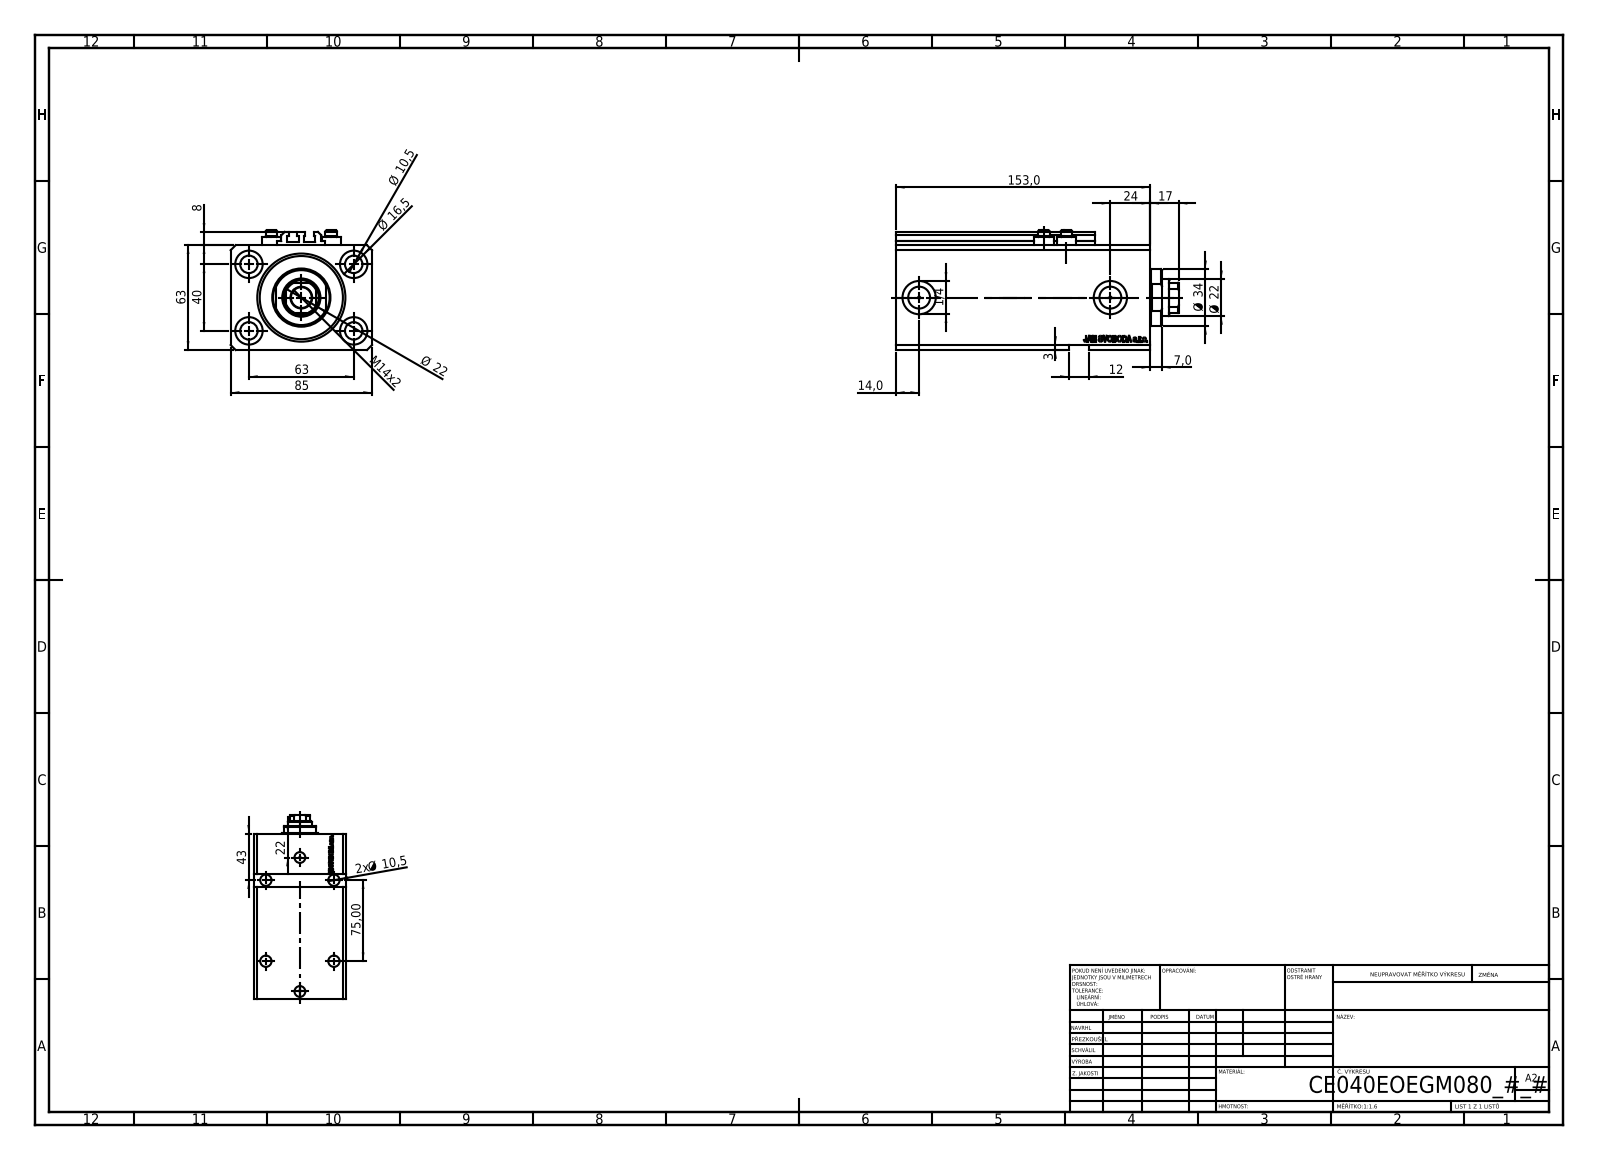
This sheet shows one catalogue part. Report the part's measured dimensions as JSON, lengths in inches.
{"part_name": "V250CE_E_Body; V250CE_C_VCP; V250CE_VC_E; ALLEN BOLT V250CE", "step_written_by": "SolidWorks 2019 (CONFIG_CONTROL_DESIGN)", "units": "inches", "bodies": {"solids": 8, "faces": 1107, "planar": 535, "cylindrical": 146, "other": 426}, "overall_size": [6.693, 3.346, 2.835], "volume_in3": 41.73, "surface_area_in2": 218.3, "round_holes": [[0.413, 8], [0.049, 4], [0.157, 4], [0.65, 4], [0.394, 2], [0.518, 2], [0.787, 2], [0.492, 1], [0.866, 1], [1.575, 1], [2.087, 1]], "round_bosses_or_shafts": [[0.457, 4], [0.276, 4], [1.339, 1]], "partial_cylinders_radius": [[0.008, 10], [0.413, 1]], "face_to_face_distances": [2.48, 3.346, 6.024, 0.669, 5.354, 0.449, 4.906, 5.575, 0.118, 2.559], "hole_center_spacings": [1.469, 2.48, 0.535, 0.606, 0.983, 1.324, 1.417, 1.491]}
